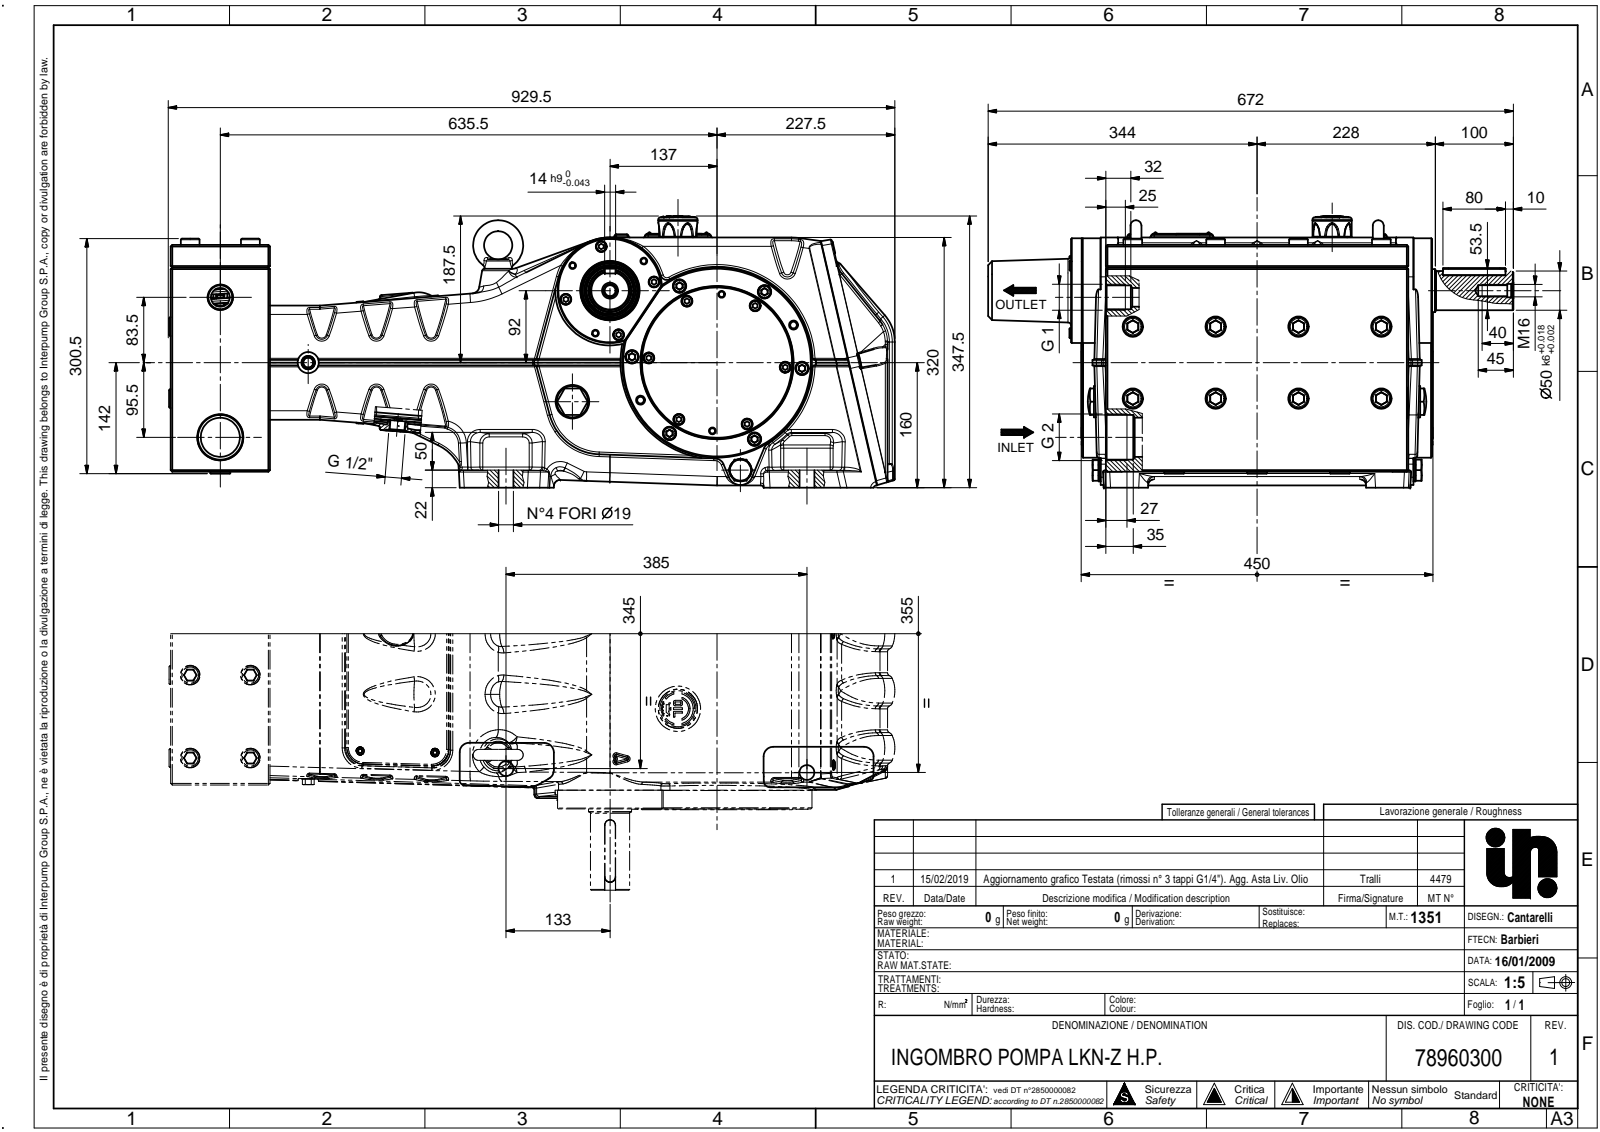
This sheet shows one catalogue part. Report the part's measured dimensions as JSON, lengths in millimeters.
{"step_written_by": "THINKDESIGN (AUTOMOTIVE_DESIGN)", "units": "millimeters", "bodies": {"solids": 141, "faces": 7555, "planar": 1656, "cylindrical": 2192, "other": 3707}, "overall_size": [928.49, 672, 347.5], "volume_mm3": 82580000, "surface_area_mm2": 3418000, "round_holes": [[8.5, 24], [14, 18], [6.75, 17], [17, 17], [5, 14], [16.5, 14], [13.5, 13], [19, 9], [25, 9], [26, 8], [7, 6], [10.5, 6]], "round_bosses_or_shafts": [[16, 24], [13, 23], [8, 23], [24, 16], [10, 14], [6, 11], [3.53, 6], [18, 5]], "partial_cylinders_radius": [[0.5, 599], [2, 171], [1.5, 103], [4, 83], [0.3, 60], [3, 50], [12, 44], [1, 32]], "face_to_face_distances": [127, 400, 38.5, 6.5, 393.5, 278.5, 317, 10, 25.1, 31.6], "hole_center_spacings": [106, 109, 65.51, 87.5, 100, 212, 57.5, 96]}
